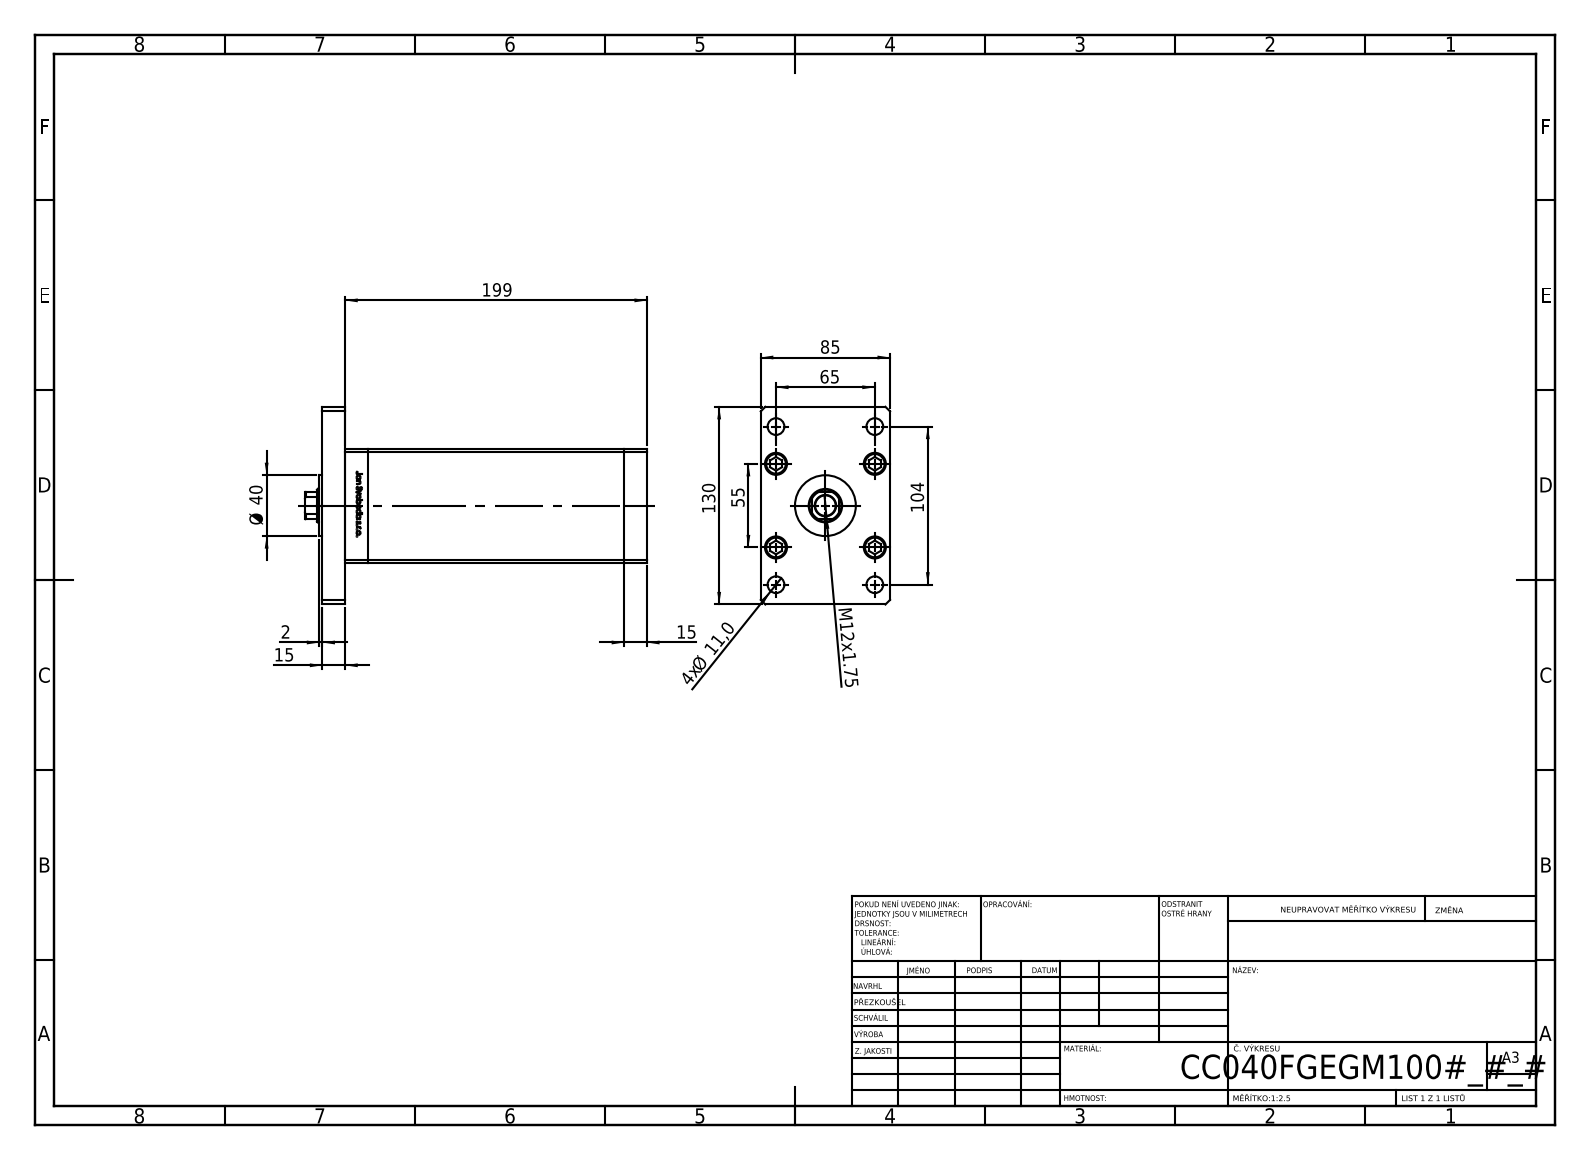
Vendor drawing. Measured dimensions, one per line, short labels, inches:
name: ALLEN BOLT; V220C_F; V220C BACK_F; V220C_VC_F (+2 more)
written by: SolidWorks 2019 (CONFIG_CONTROL_DESIGN)
unit: in
bodies: 18 solids, 1307 faces (514 planar, 187 cylindrical, 606 other)
size: 8.858 × 5.118 × 3.346
volume: 72.19 in³; area: 324.8 in²
holes: 9× ⌀0.433, 5× ⌀0.61, 4× ⌀0.394, 4× ⌀0.571, 2× ⌀0.079, 2× ⌀0.518, 1× ⌀0.531, 1× ⌀0.866, 1× ⌀0.925
bosses: 9× ⌀0.315, 5× ⌀0.571, 1× ⌀1.575
rounds: 2× R0.037, 1× R0.413
face distances: 0.591, 3.346, 7.224, 7.815, 2.953, 1.181, 6.634, 8.406, 0.413, 1.083
hole spacings: 1.102, 0.965, 1.676, 2.414, 2.559, 2.735, 3.13, 4.043
